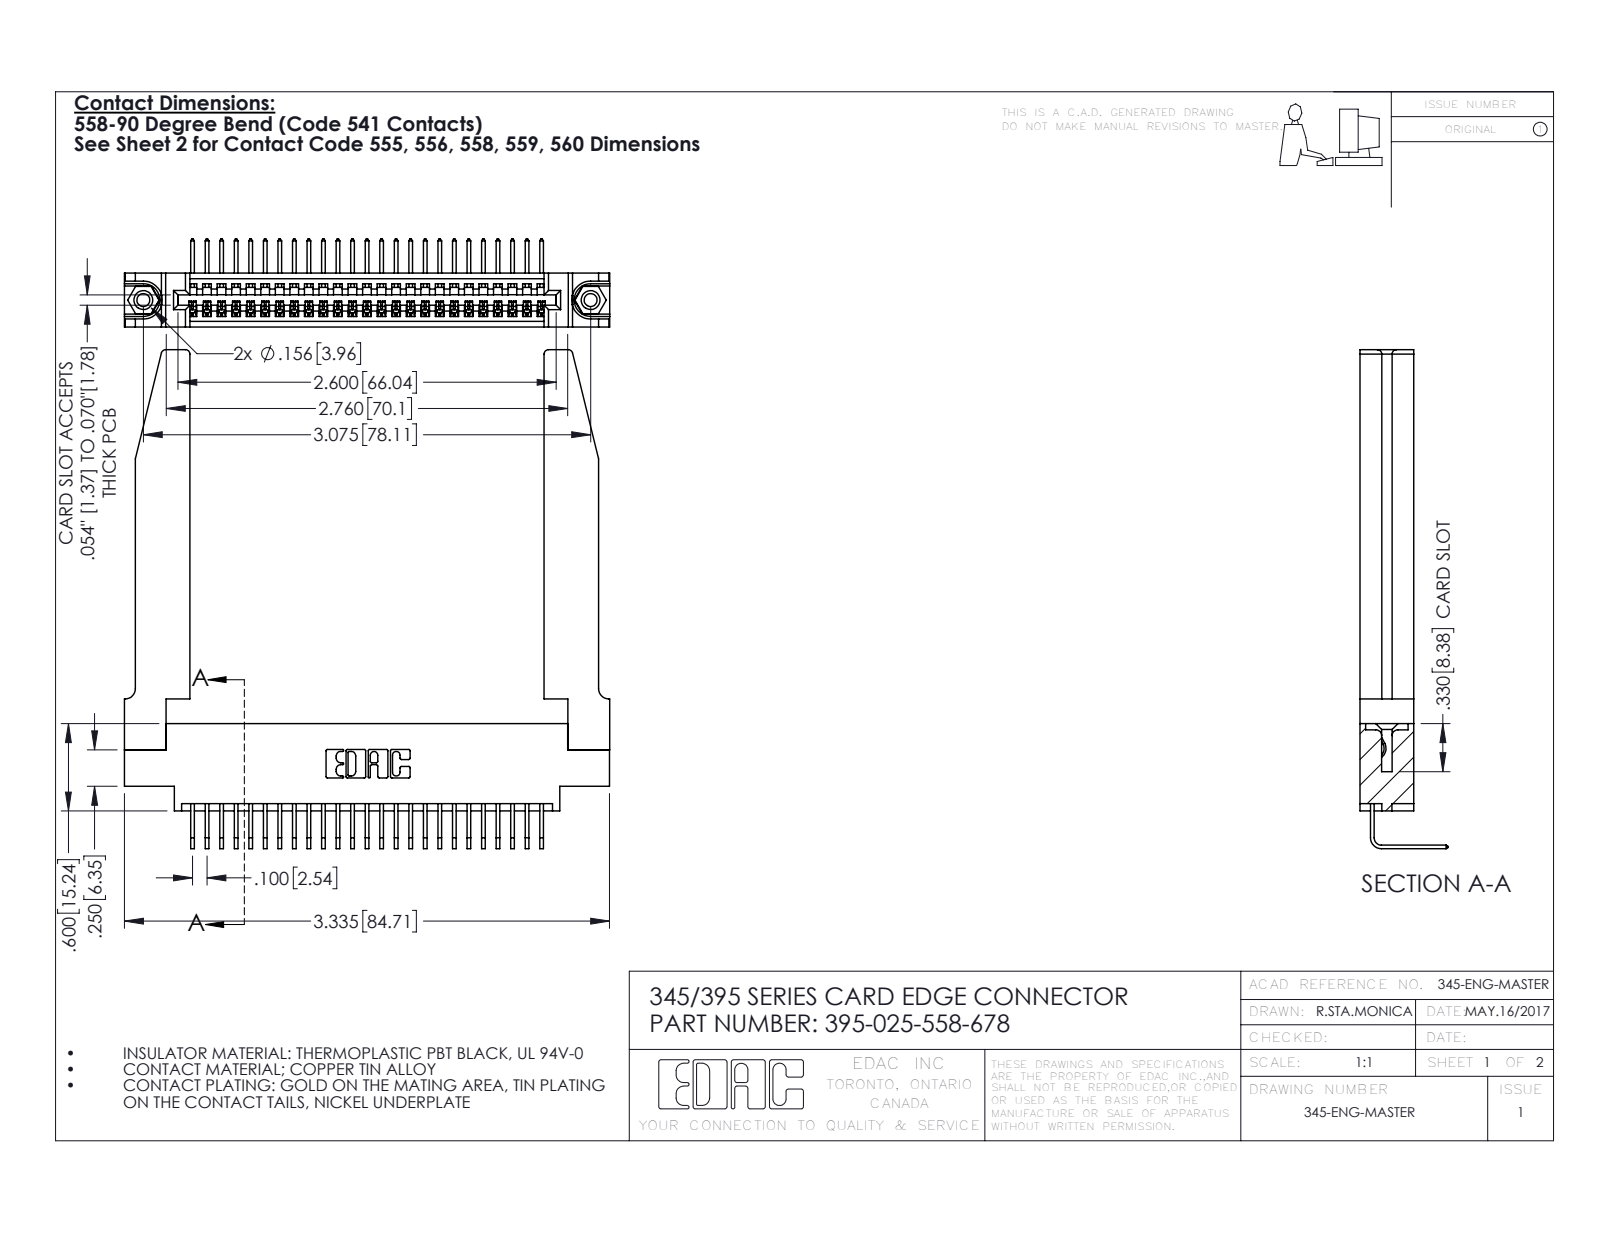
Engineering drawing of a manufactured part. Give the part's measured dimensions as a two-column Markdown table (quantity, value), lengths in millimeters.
| quantity | value |
| --- | --- |
| part name | 345-220-078_345-220-078; 395-025-558-678; 345 Part_0.170 Offset - 0.156 Dia-TH; 345-250-001_345-250-001-102 (+1 more) |
| STEP written by | SolidWorks 2016 (CONFIG_CONTROL_DESIGN) |
| units | millimeters |
| bodies | 30 solids, 1864 faces (1276 planar, 536 cylindrical, 52 other) |
| overall size | 87.1 × 84.7 × 15.4 |
| volume | 15 600 mm³ |
| surface area | 17 700 mm² |
| round holes (diameter × count) | 2.3 × 2, 3.2 × 2, 4 × 2, 1.6 × 1 |
| round bosses / shafts (diameter × count) | 3.9 × 2 |
| partial cylindrical surfaces (radius × count) | 0.2 × 50, 0.3 × 22, 0.8 × 8, 0.2 × 6, 0.8 × 6, 0.7 × 3, 0.8 × 2, 1 × 2 |
| main face-to-face distances | 9.4, 1.8, 7.6, 2.5, 6.9, 0.6, 5.1, 3.8, 3.8, 5.7 |
| hole center spacings | 6.9, 72.1, 78.1 |
